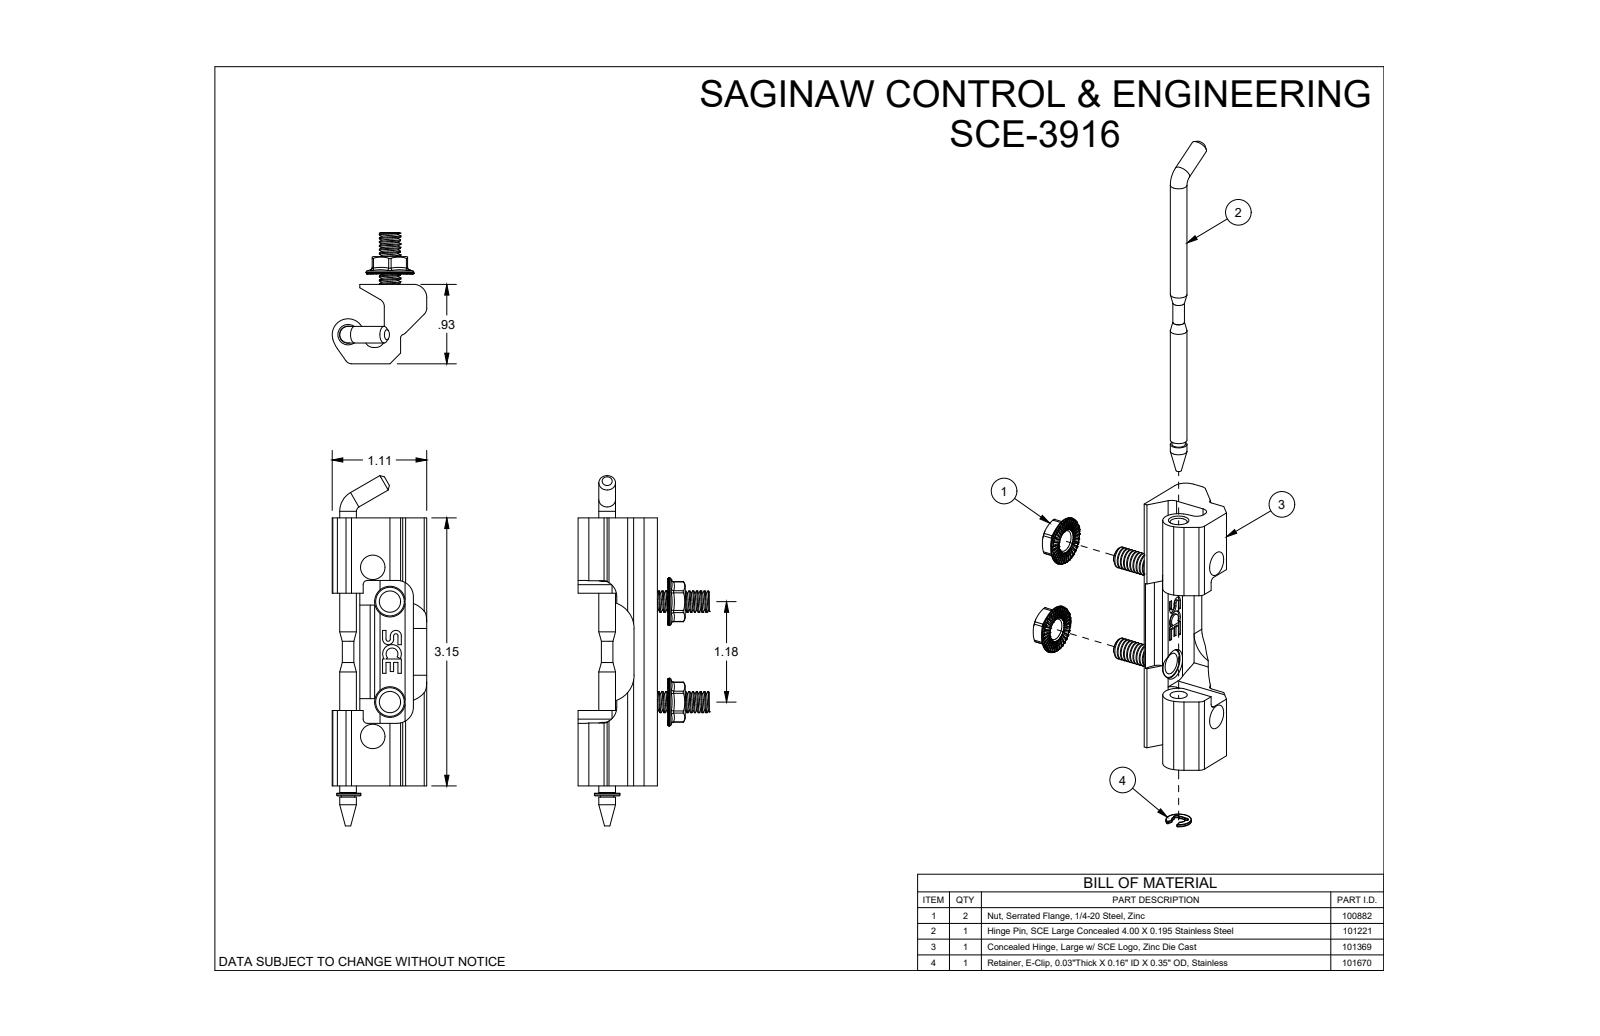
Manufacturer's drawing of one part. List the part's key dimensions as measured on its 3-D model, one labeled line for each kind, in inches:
Part name (STEP PRODUCT): SCE-3916
STEP written by: SolidWorks 2019 (CONFIG_CONTROL_DESIGN)
Units: inches
Bodies: 7 solids, 683 faces (232 planar, 110 cylindrical, 341 other)
Overall size (bounding box): 4.118 × 1.543 × 1.112
Volume: 1.248 in³ · Surface area: 19.87 in²
Round holes (diameter × count): ⌀0.25 ×2, ⌀0.25 ×2, ⌀0.36 ×2, ⌀0.04 ×1, ⌀0.201 ×1
Round bosses / shafts (diameter × count): ⌀0.563 ×2, ⌀0.337 ×2, ⌀0.248 ×2, ⌀0.196 ×2, ⌀0.3 ×1, ⌀0.157 ×1, ⌀0.136 ×1
Partial cylindrical surfaces — rounded edges, fillets, slot ends (radius × count): R0.029 ×12, R0.01 ×3, R0.098 ×3, R0.1 ×3, R0.005 ×2, R0.025 ×2, R0.03 ×2, R0.05 ×2
Main face-to-face distances: 0.933, 3.15, 0.499, 0.192, 0.735, 2.415, 0.14, 0.793, 0.307, 0.127
Hole centre spacings: 0.592, 1.181
